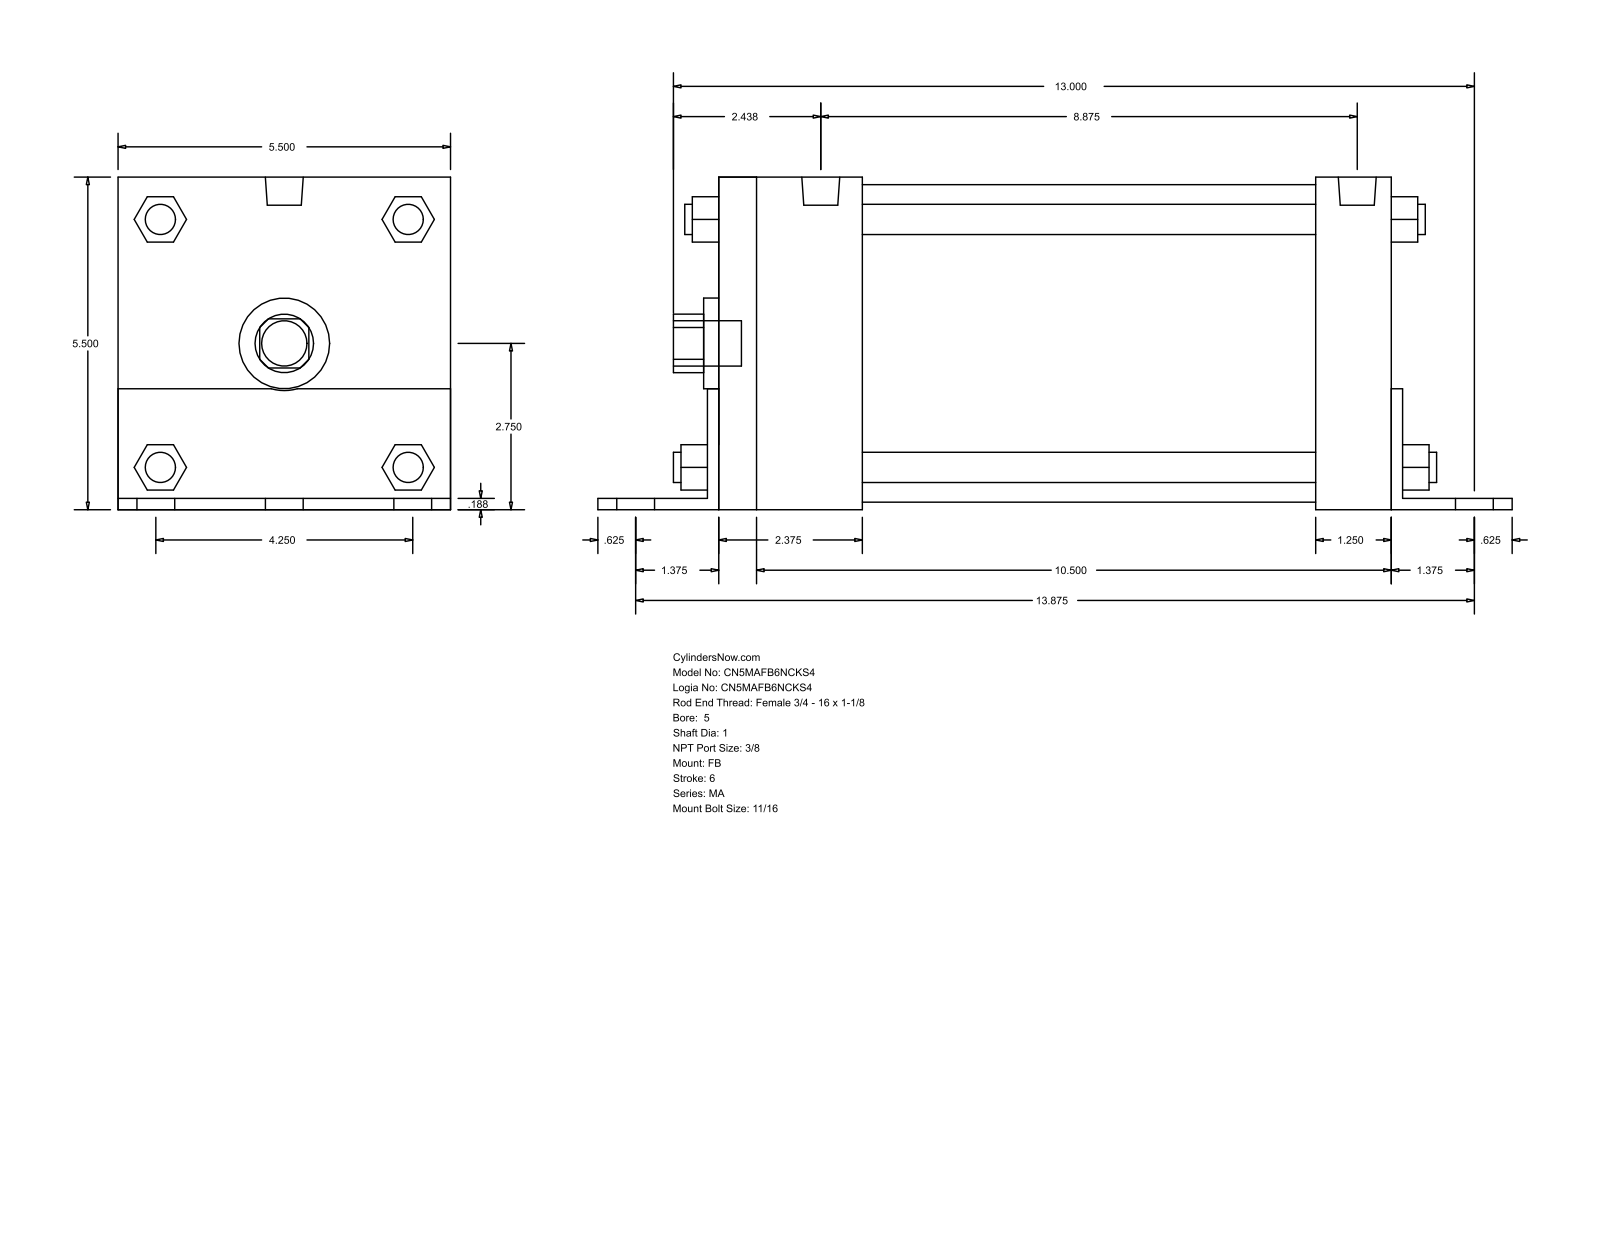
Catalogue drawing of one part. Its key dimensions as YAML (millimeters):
part_name: "MA_FB__0500_1"
step_written_by: "GSSL Pune (CONFIG_CONTROL_DESIGN)"
units: millimeters
bodies: {solids: 0, faces: 140, planar: 105, cylindrical: 35, other: 0}
overall_size: [384.18, 139.75, 139.7]
round_holes:
  - {diameter: 25.4, count: 1}
  - {diameter: 38.1, count: 1}
  - {diameter: 133.35, count: 1}
round_bosses_or_shafts:
  - {diameter: 17.46, count: 6}
  - {diameter: 12.7, count: 4}
  - {diameter: 11.11, count: 4}
  - {diameter: 15.93, count: 2}
  - {diameter: 19.05, count: 1}
partial_cylinders:
  - {radius: 12.29, count: 1}
  - {radius: 19.81, count: 1}
face_to_face_distances: [139.7, 4.76, 139.75, 4.71, 134.99, 282.57, 4.77, 287.34, 287.33, 292.1]
